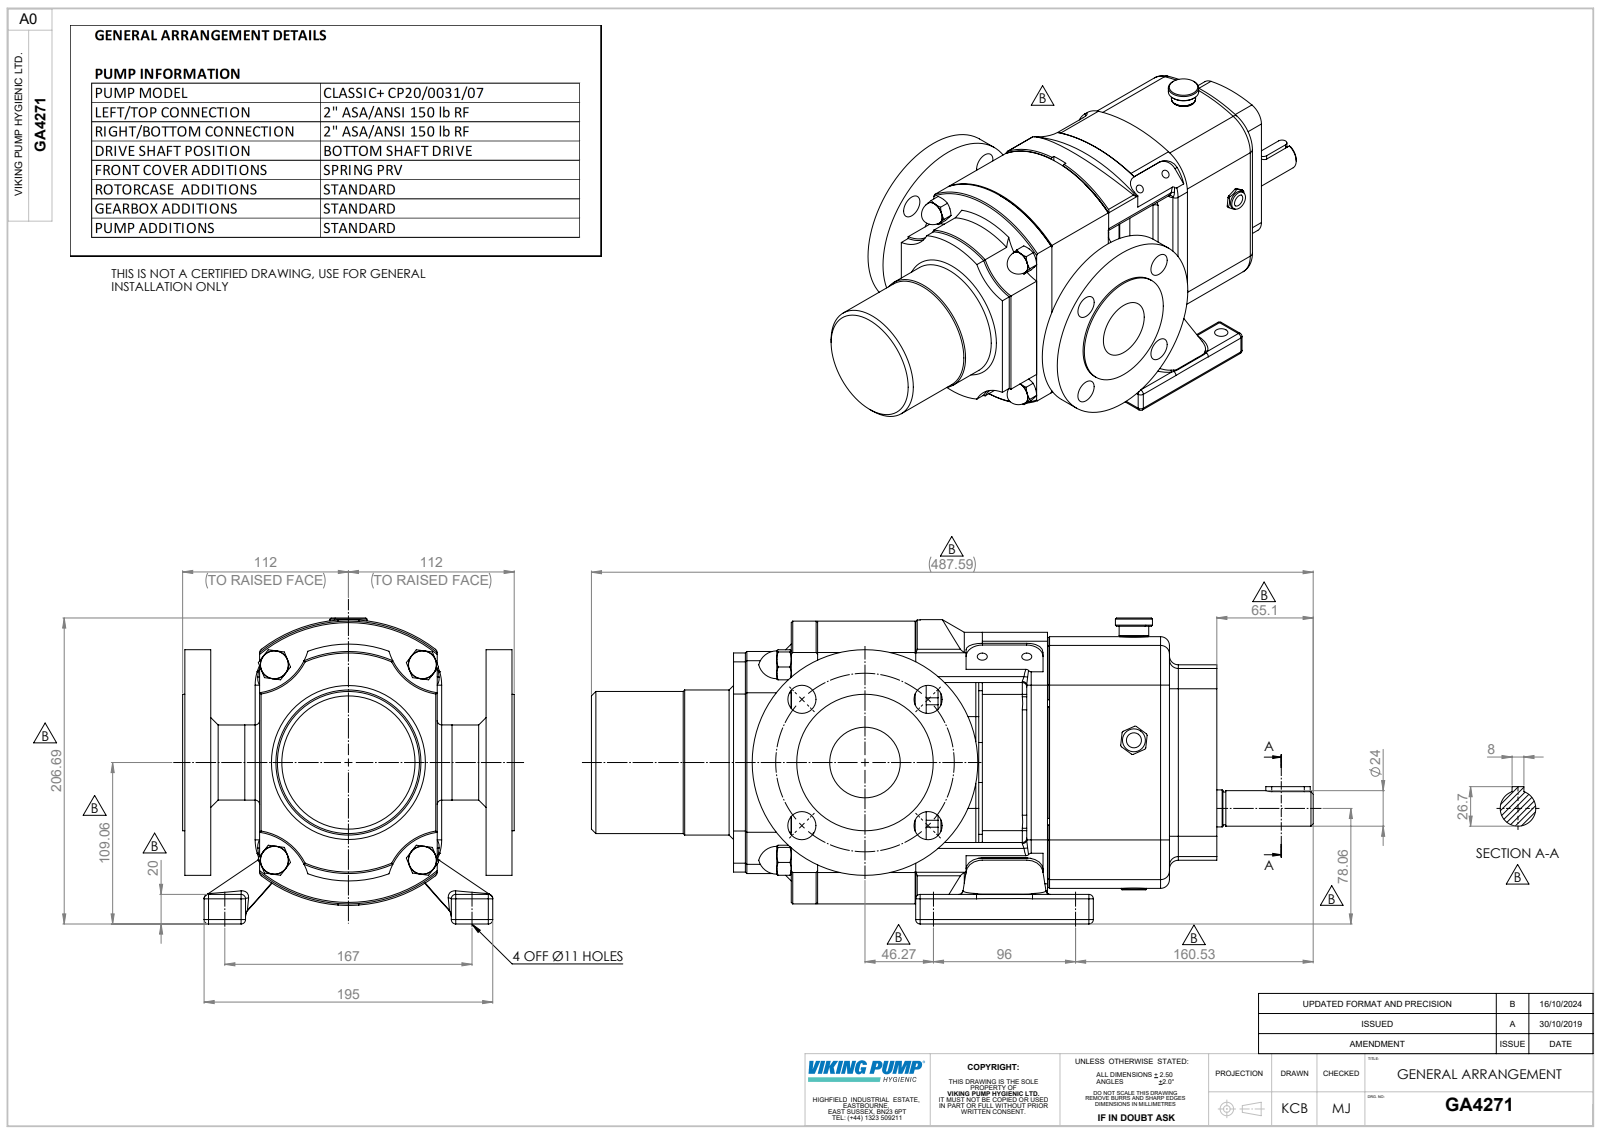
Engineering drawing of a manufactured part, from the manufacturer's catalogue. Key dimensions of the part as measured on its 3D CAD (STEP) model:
Part name (STEP PRODUCT): Copy of MP-CP20 Spring PRV^GA4271; Copy of Z94-5301-33 - 2 INCH ASA 150^GA4271; GA4271; Copy of CP20-0031-07 H B^GA4271
STEP written by: SolidWorks 2023 (AUTOMOTIVE_DESIGN)
Units: millimetres
Bodies: 4 solids, 874 faces (266 planar, 325 cylindrical, 283 other)
Overall size (bounding box): 487.59 × 224 × 206.69
Volume: 7 051 000 mm³ · Surface area: 476 605 mm²
Round holes (diameter × count): ⌀19 ×6, ⌀6.8 ×4, ⌀11 ×4, ⌀6.47 ×3, ⌀8 ×2, ⌀22.53 ×1, ⌀47.7 ×1
Round bosses / shafts (diameter × count): ⌀35 ×2, ⌀17 ×2, ⌀152.4 ×1, ⌀98 ×1, ⌀96 ×1, ⌀92.2 ×1, ⌀50.8 ×1, ⌀50.7 ×1
Partial cylindrical surfaces — rounded edges, fillets, slot ends (radius × count): R3 ×52, R2 ×18, R1 ×12, R6 ×8, R11.1 ×8, R1.27 ×6, R4 ×6, R8 ×6
Main face-to-face distances: 33, 153, 120, 17.5, 50.5, 170.5, 203.5, 186, 221, 19
Hole centre spacings: 60.3, 120.6, 53.7, 30.05, 60.29, 85.23, 85.27, 85.28
